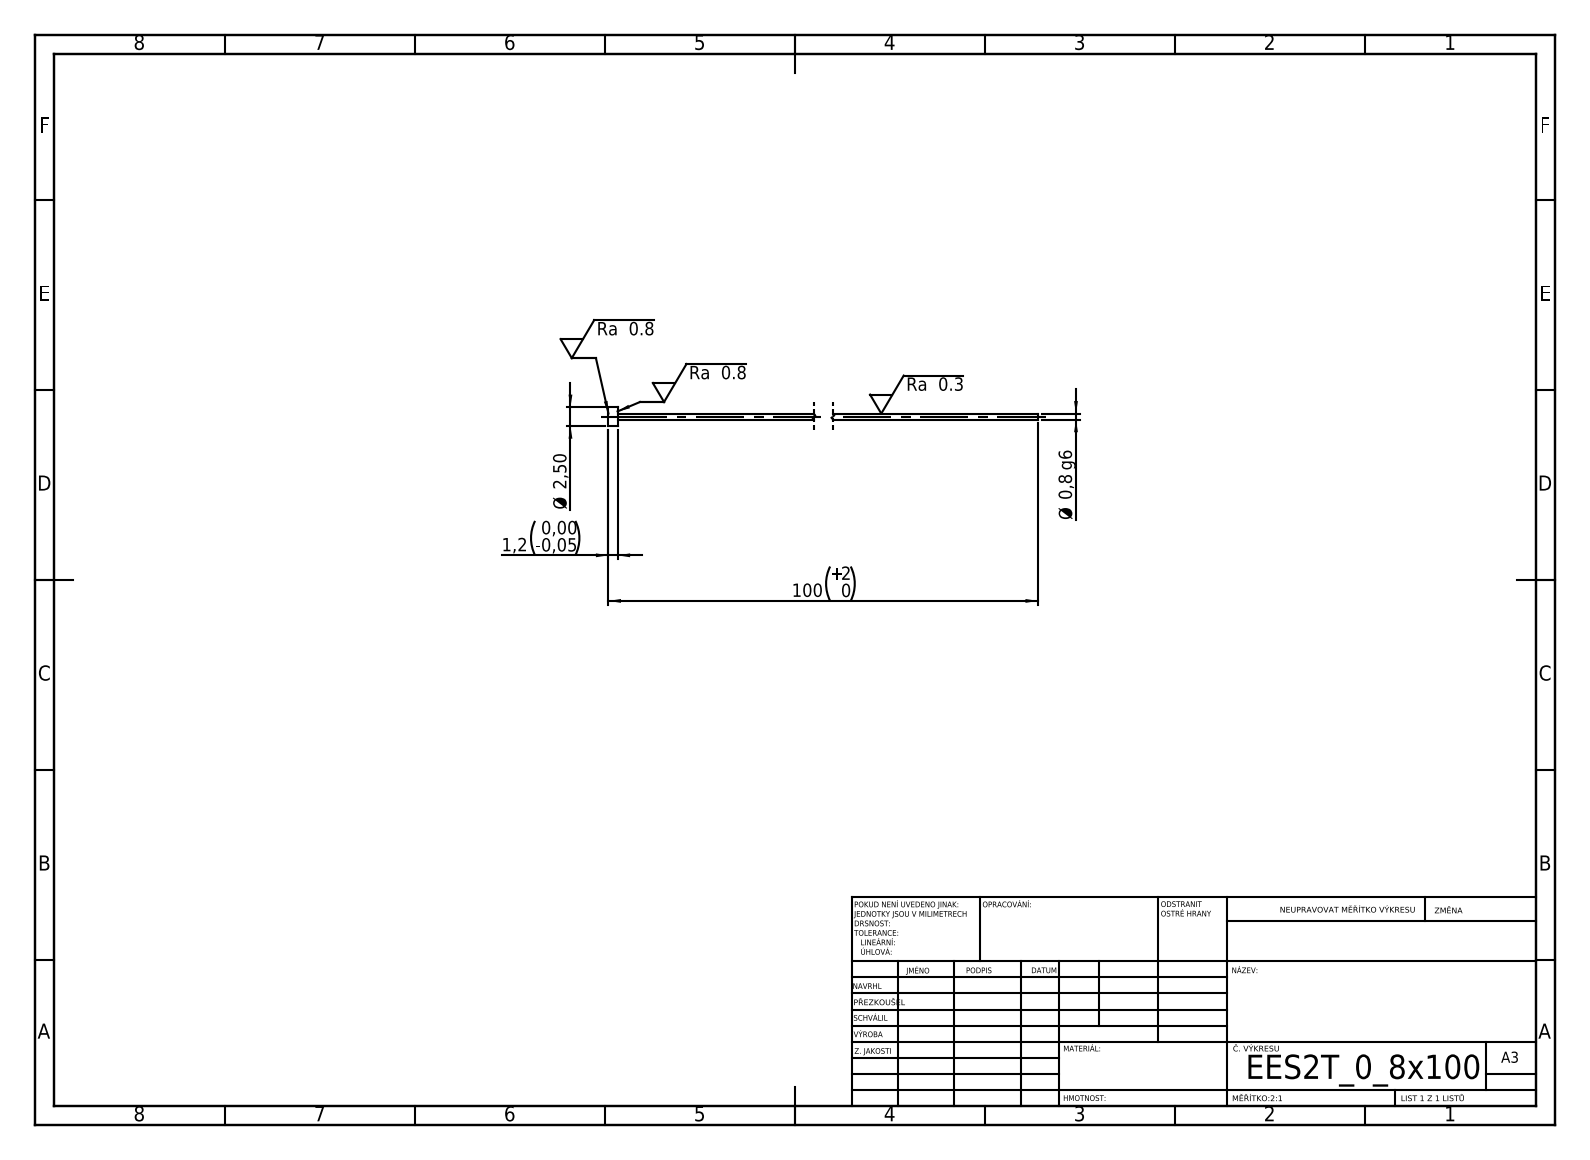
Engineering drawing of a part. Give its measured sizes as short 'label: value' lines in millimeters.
written by: SolidWorks 2019 (CONFIG_CONTROL_DESIGN)
unit: mm
bodies: 1 solid, 7 faces (3 planar, 4 cylindrical, 0 other)
size: 100 × 2.5 × 2.5
volume: 56 mm³; area: 268 mm²
bosses: 1× ⌀2.5, 1× ⌀0.8
face distances: 1.2, 100, 98.8
